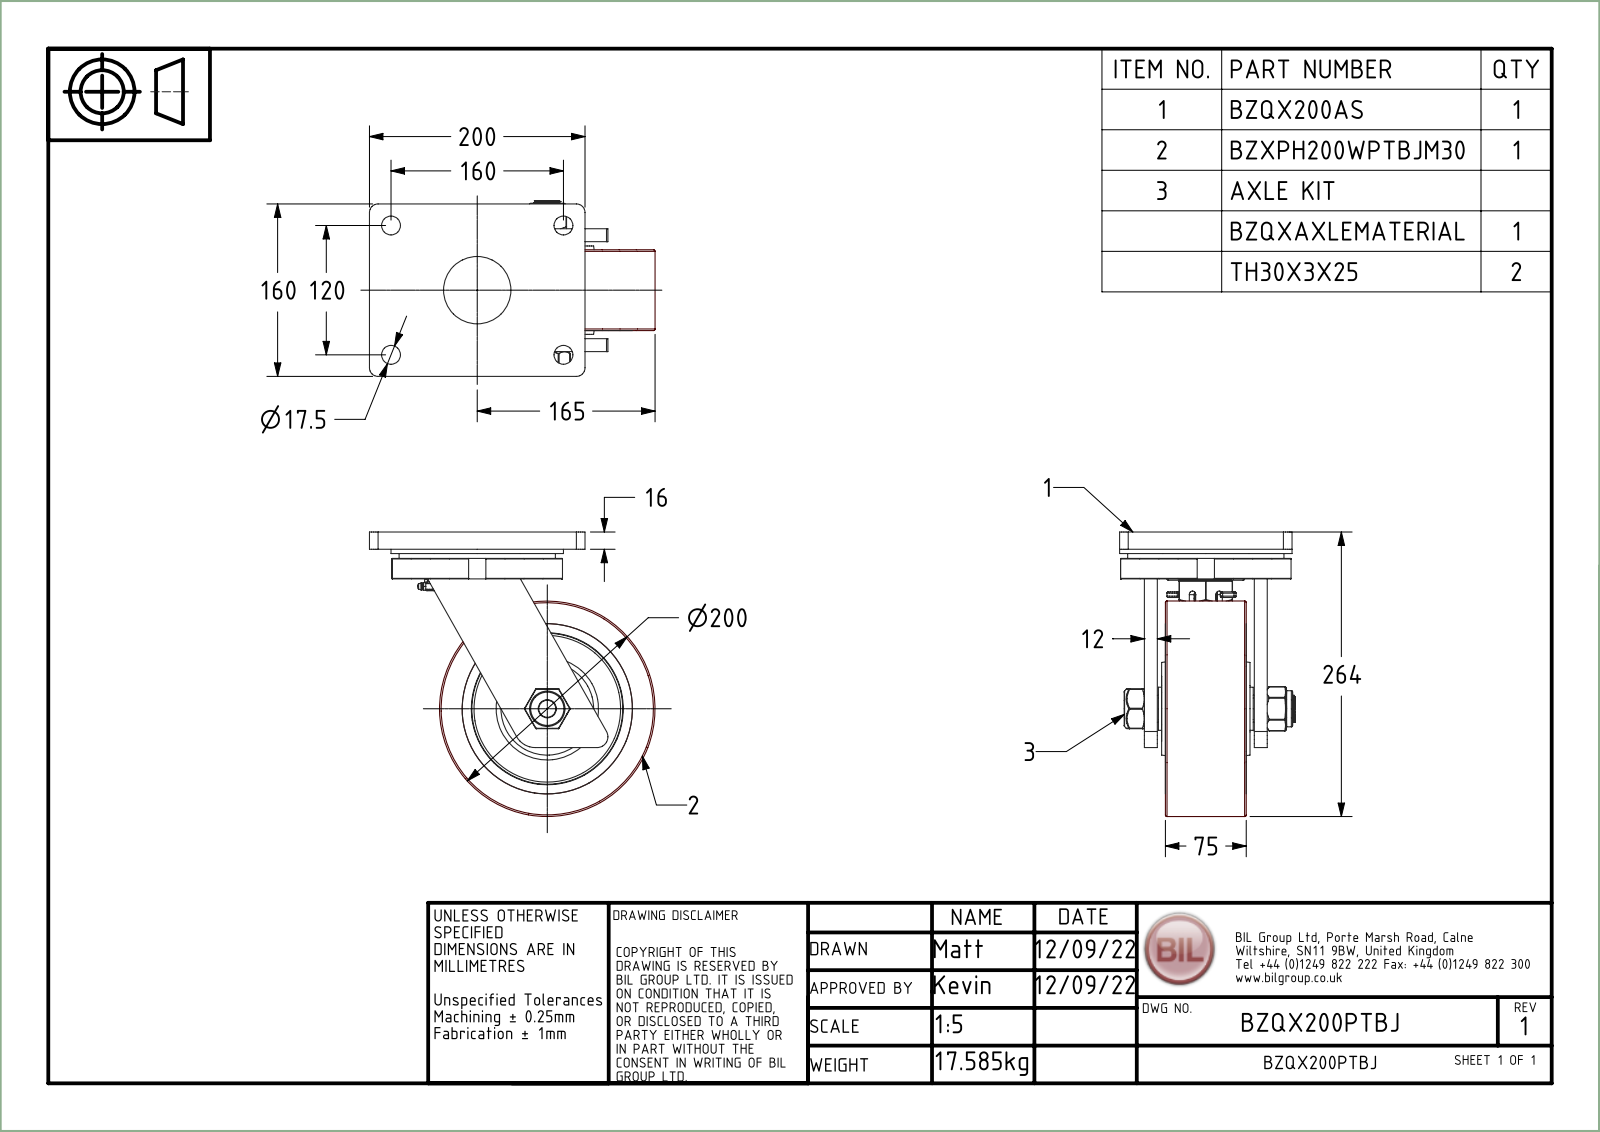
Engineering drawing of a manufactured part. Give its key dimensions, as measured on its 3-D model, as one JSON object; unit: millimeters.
{"part_name": "BZQX200AS; FABRICATED STEEL TOP PLATE; FABRICATED STEEL FORKS; FABRICATED STEEL FORKS Geometry (+8 more)", "step_written_by": "Spatial InterOp 3D (AUTOMOTIVE_DESIGN)", "units": "millimeters", "bodies": {"solids": 41, "faces": 1238, "planar": 304, "cylindrical": 410, "other": 524}, "overall_size": [265, 264, 163.75], "volume_mm3": 3156000, "surface_area_mm2": 550588, "round_holes": [[17.5, 4], [4, 1], [5.4, 1], [8, 1], [15.8, 1], [25, 1], [25.5, 1], [26, 1], [29, 1], [30, 1], [32, 1], [40.36, 1]], "round_bosses_or_shafts": [[200, 1], [160, 1], [159, 1], [145, 1], [54, 1], [52.97, 1], [52.5, 1], [42.76, 1]], "partial_cylinders_radius": [[1.25, 22], [1, 20], [0.5, 12], [2, 6], [8, 4], [3.38, 3], [0.22, 2], [0.22, 2]], "face_to_face_distances": [16, 12, 51, 43.5, 19.5, 94.5, 102, 7.5, 82.5, 39], "hole_center_spacings": [100, 85.25, 120, 120.83, 160, 200, 30.55, 124.24]}
